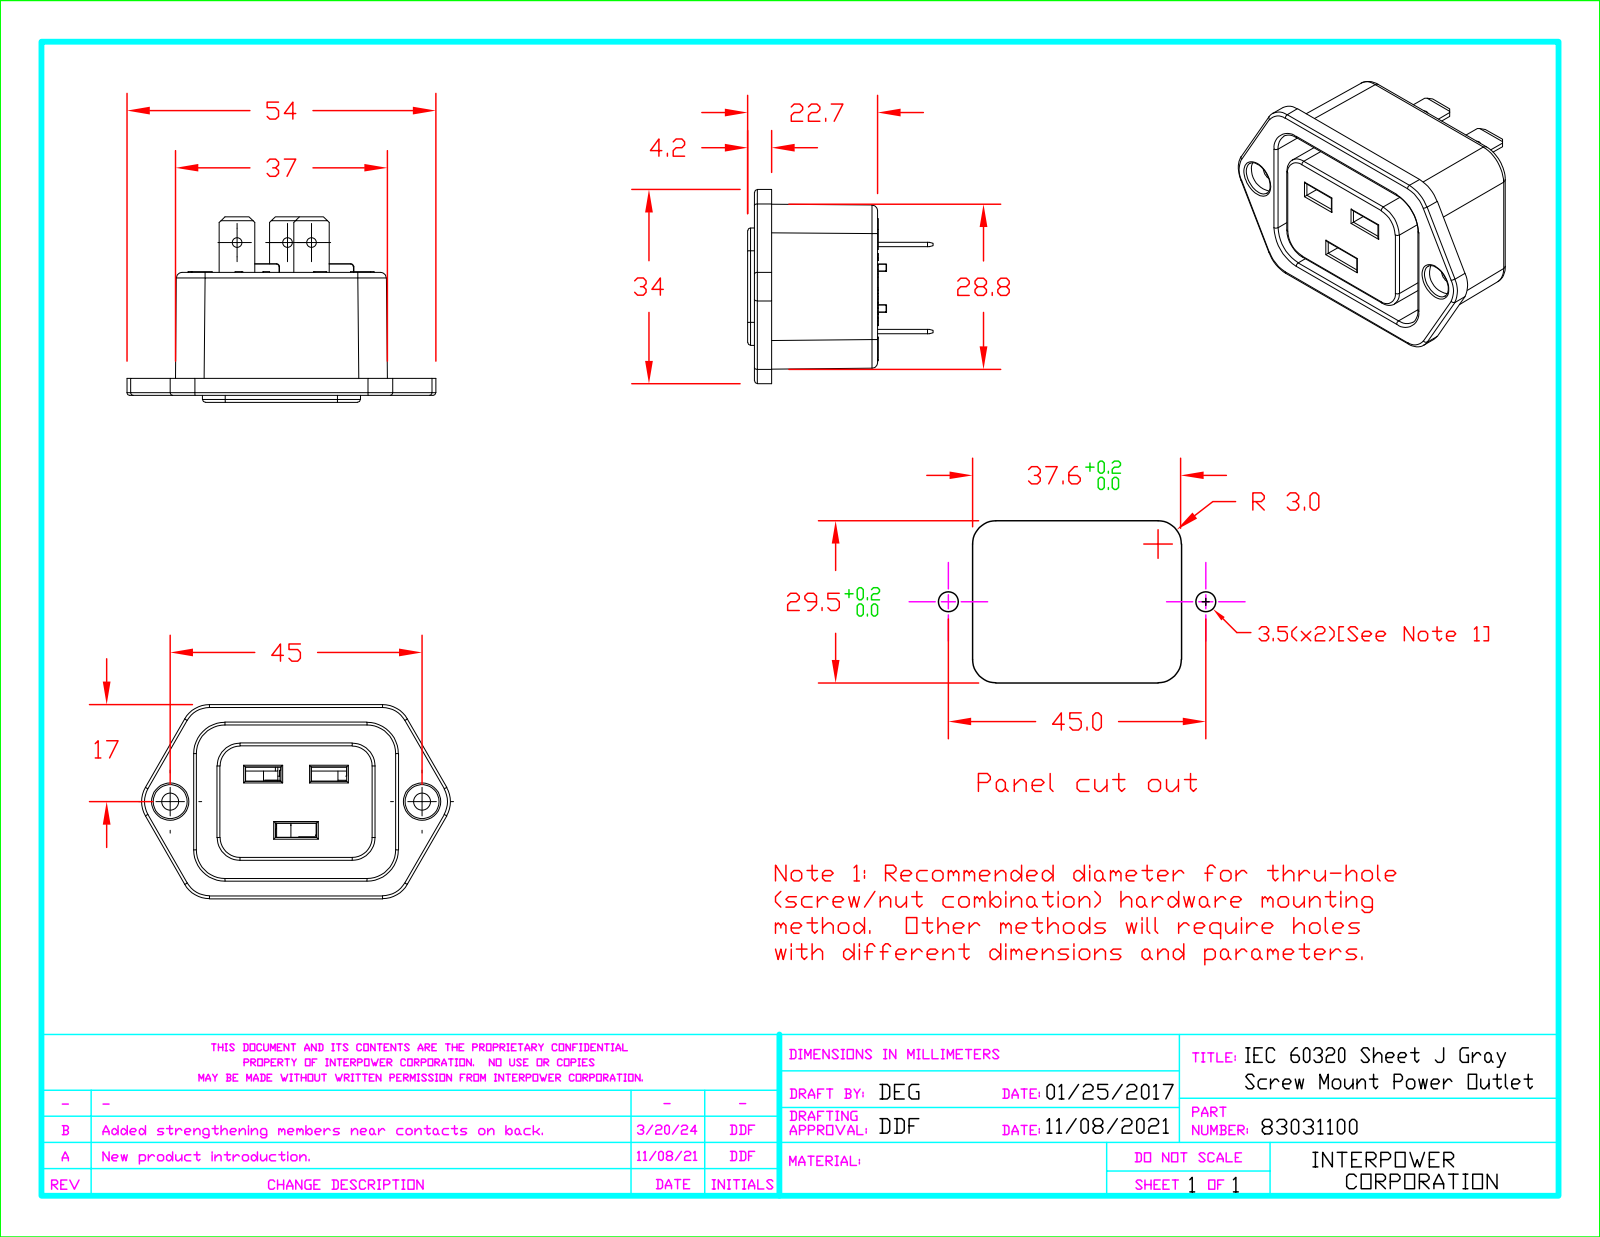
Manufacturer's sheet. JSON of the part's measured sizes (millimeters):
{"part_name": "68024170_R8_Hsng_Sheet-J_SM_Solder-Outlet_1-20-17; Part-Number-Insert_83031000; 68024150_R10_Hsng_Sheet-J_SM_QD-Outlet_1-20-17; 55020620_R9_Sheet-J_6.3-QD_2-28-16 (+2 more)", "step_written_by": "PTC Creo Elements/Direct Modeling 19.0D 23-Nov-2015 (C) Parametric Technology GmbH (AUTOMOTIVE_DESIGN)", "units": "millimeters", "bodies": {"solids": 5, "faces": 1491, "planar": 974, "cylindrical": 458, "other": 59}, "overall_size": [54, 34, 32.79], "volume_mm3": 11747, "surface_area_mm2": 16134, "round_holes": [[1.8, 3], [6, 2], [0.52, 1], [4, 1]], "partial_cylinders_radius": [[0.5, 47], [0.4, 36], [1.2, 36], [0.36, 18], [0.23, 16], [0.73, 16], [0.78, 16], [4.5, 14]], "face_to_face_distances": [0.8, 1.5, 18.5, 20, 4.38, 3, 21.5, 22.88, 1.38, 8], "hole_center_spacings": [4.39, 8.6, 10.91, 12.99, 13.76, 16.88, 36.68, 37.64]}
